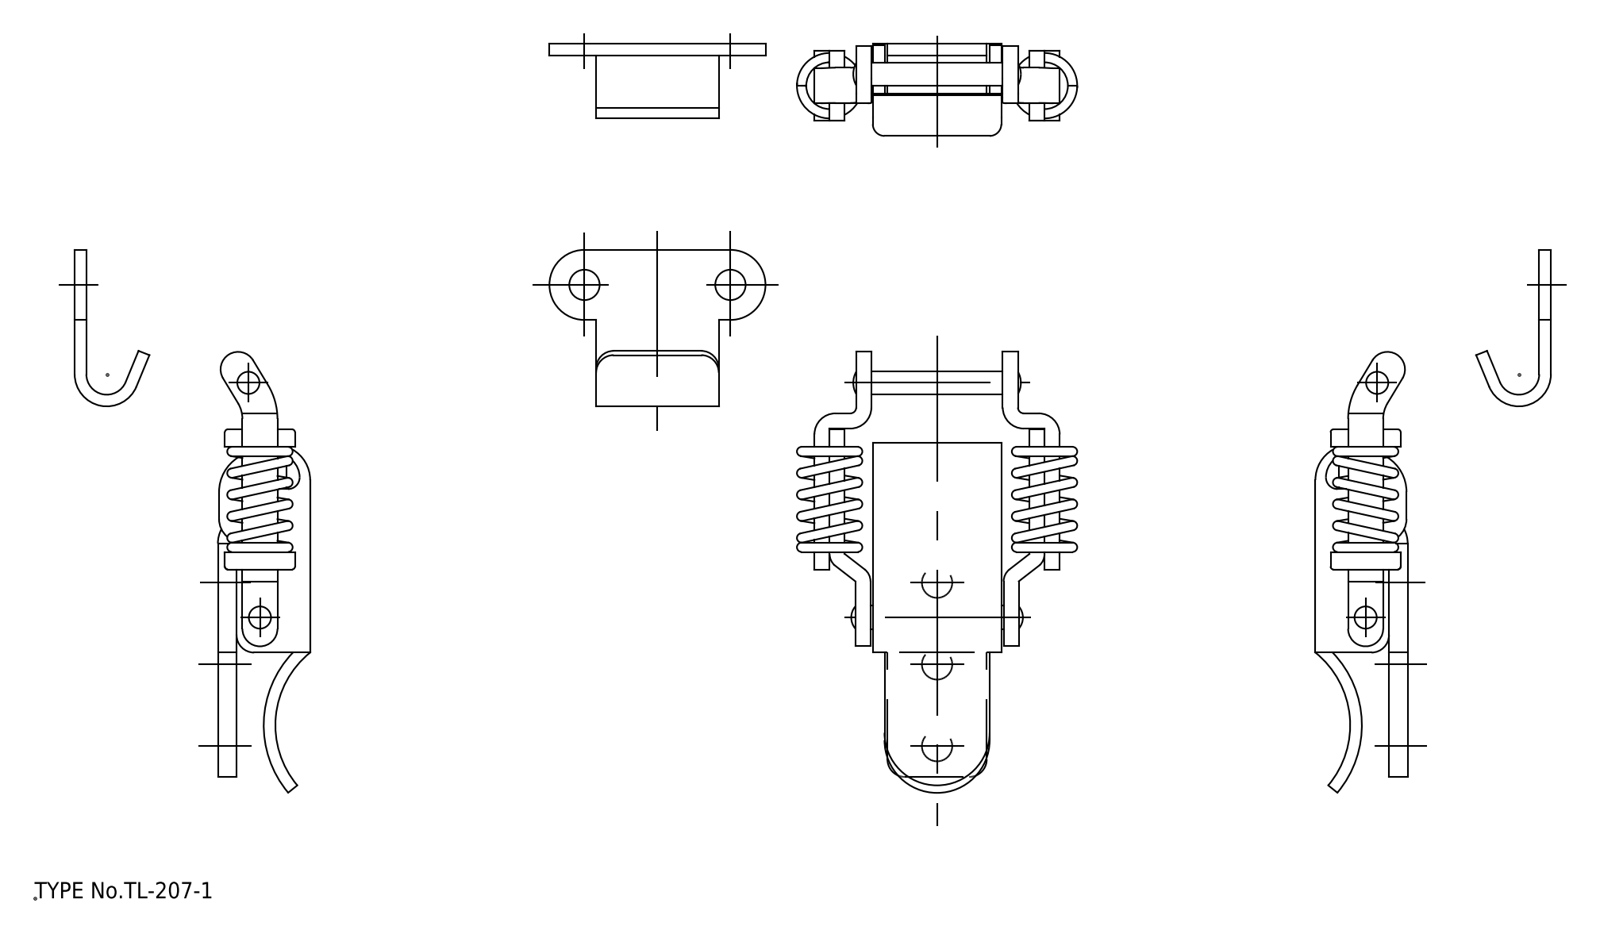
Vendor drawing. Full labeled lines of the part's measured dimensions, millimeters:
Part name (STEP PRODUCT): ベース; レバー; スプリング; アームA (+2 more)
STEP written by: spGate 19.8.4 (****-****-****-****) (AUTOMOTIVE_DESIGN)
Units: millimetres
Bodies: 9 solids, 232 faces (119 planar, 79 cylindrical, 34 other)
Overall size (bounding box): 92.97 × 48.01 × 15.8
Volume: 12 980 mm³ · Surface area: 14 592 mm²
Round holes (diameter × count): ⌀5.2 ×5, ⌀4.18 ×1
Round bosses / shafts (diameter × count): ⌀4 ×2
Partial cylindrical surfaces — rounded edges, fillets, slot ends (radius × count): R3 ×7, R2 ×5, R0.5 ×4, R2.6 ×4, R3.6 ×4, R1 ×3, R6 ×3, R4 ×2
Main face-to-face distances: 2, 3.2, 2.6, 20, 7.4, 9.4, 27.4, 29.4, 36.8, 1.2
Hole centre spacings: 14, 52.51, 66.19, 79.98, 25, 28
